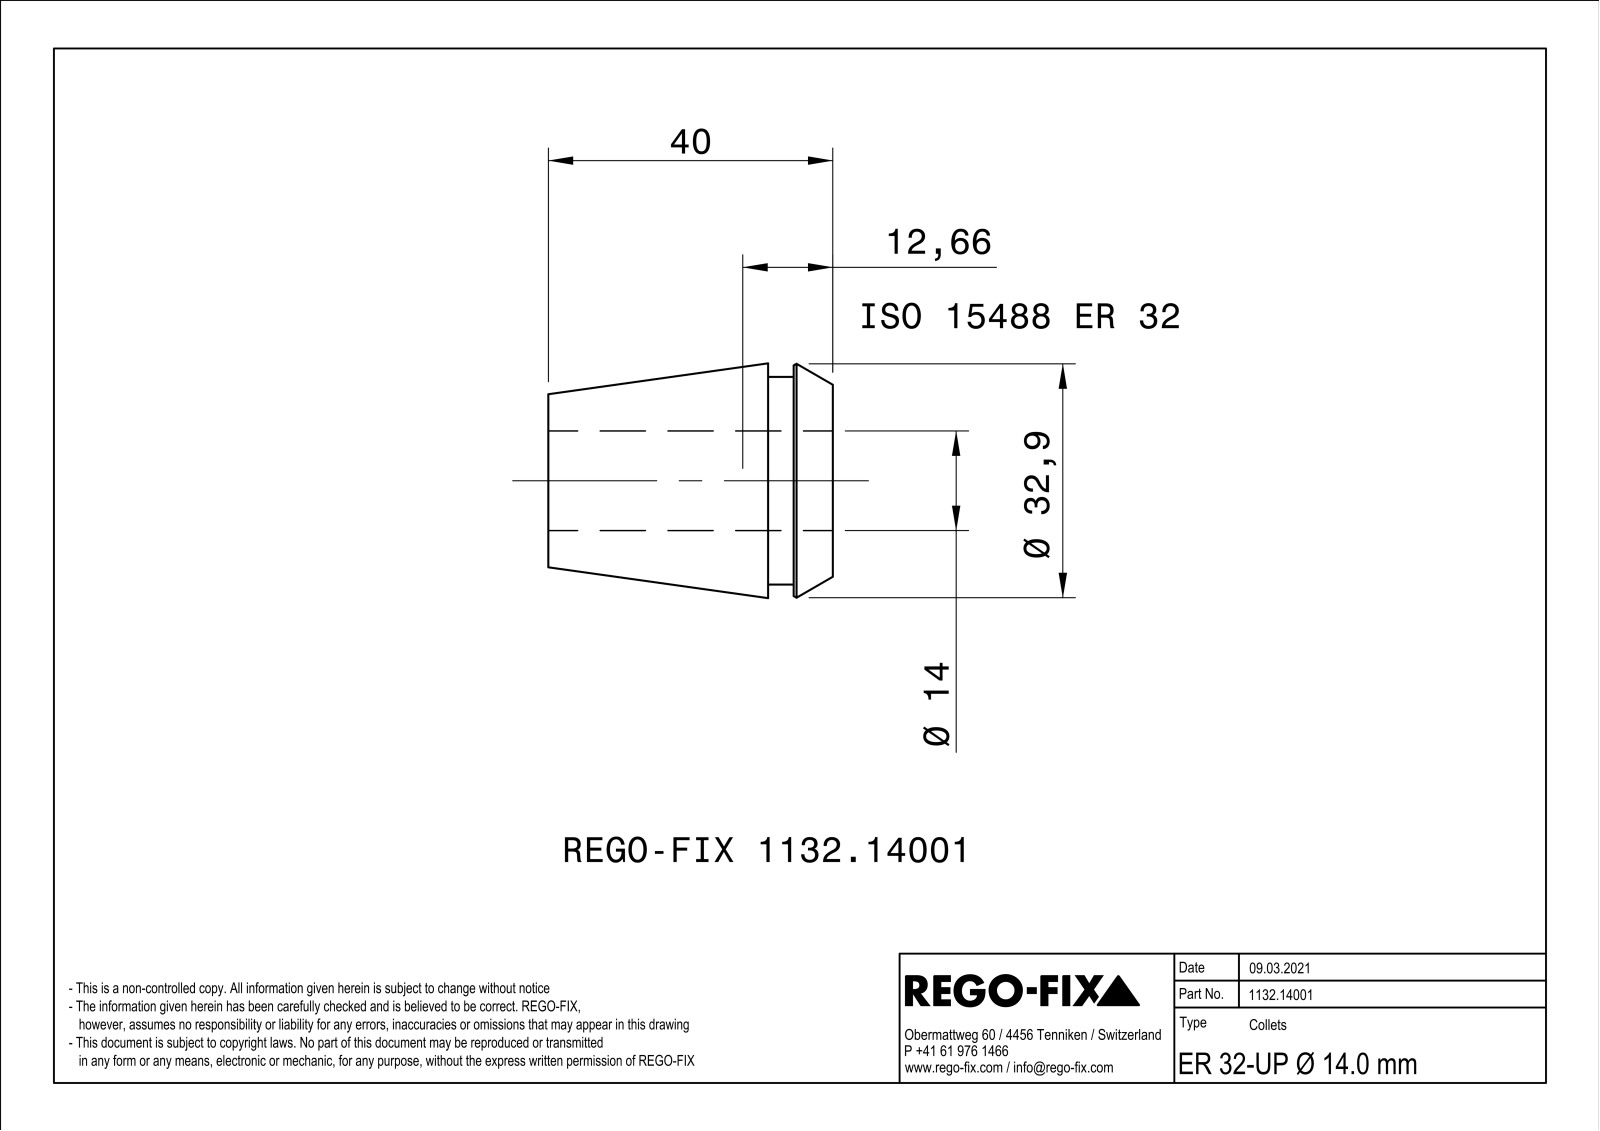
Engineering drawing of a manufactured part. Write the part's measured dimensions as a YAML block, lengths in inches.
part_name: "NOCUT"
step_written_by: "SIEMENS PLM Software Solid Edge ST10 (AUTOMOTIVE_DESIGN)"
units: inches
bodies: {solids: 1, faces: 209, planar: 88, cylindrical: 41, other: 80}
overall_size: [1.575, 1.298, 1.298]
volume: 0.978
surface_area: 21.47
round_holes:
  - {diameter: 0.551, count: 1}
round_bosses_or_shafts:
  - {diameter: 1.15, count: 1}
partial_cylinders:
  - {radius: 0.016, count: 20}
face_to_face_distances: [0.039, 1.575, 0.358, 1.217, 0.217, 0.142, 1.358, 0.236, 0.02, 0.122]
